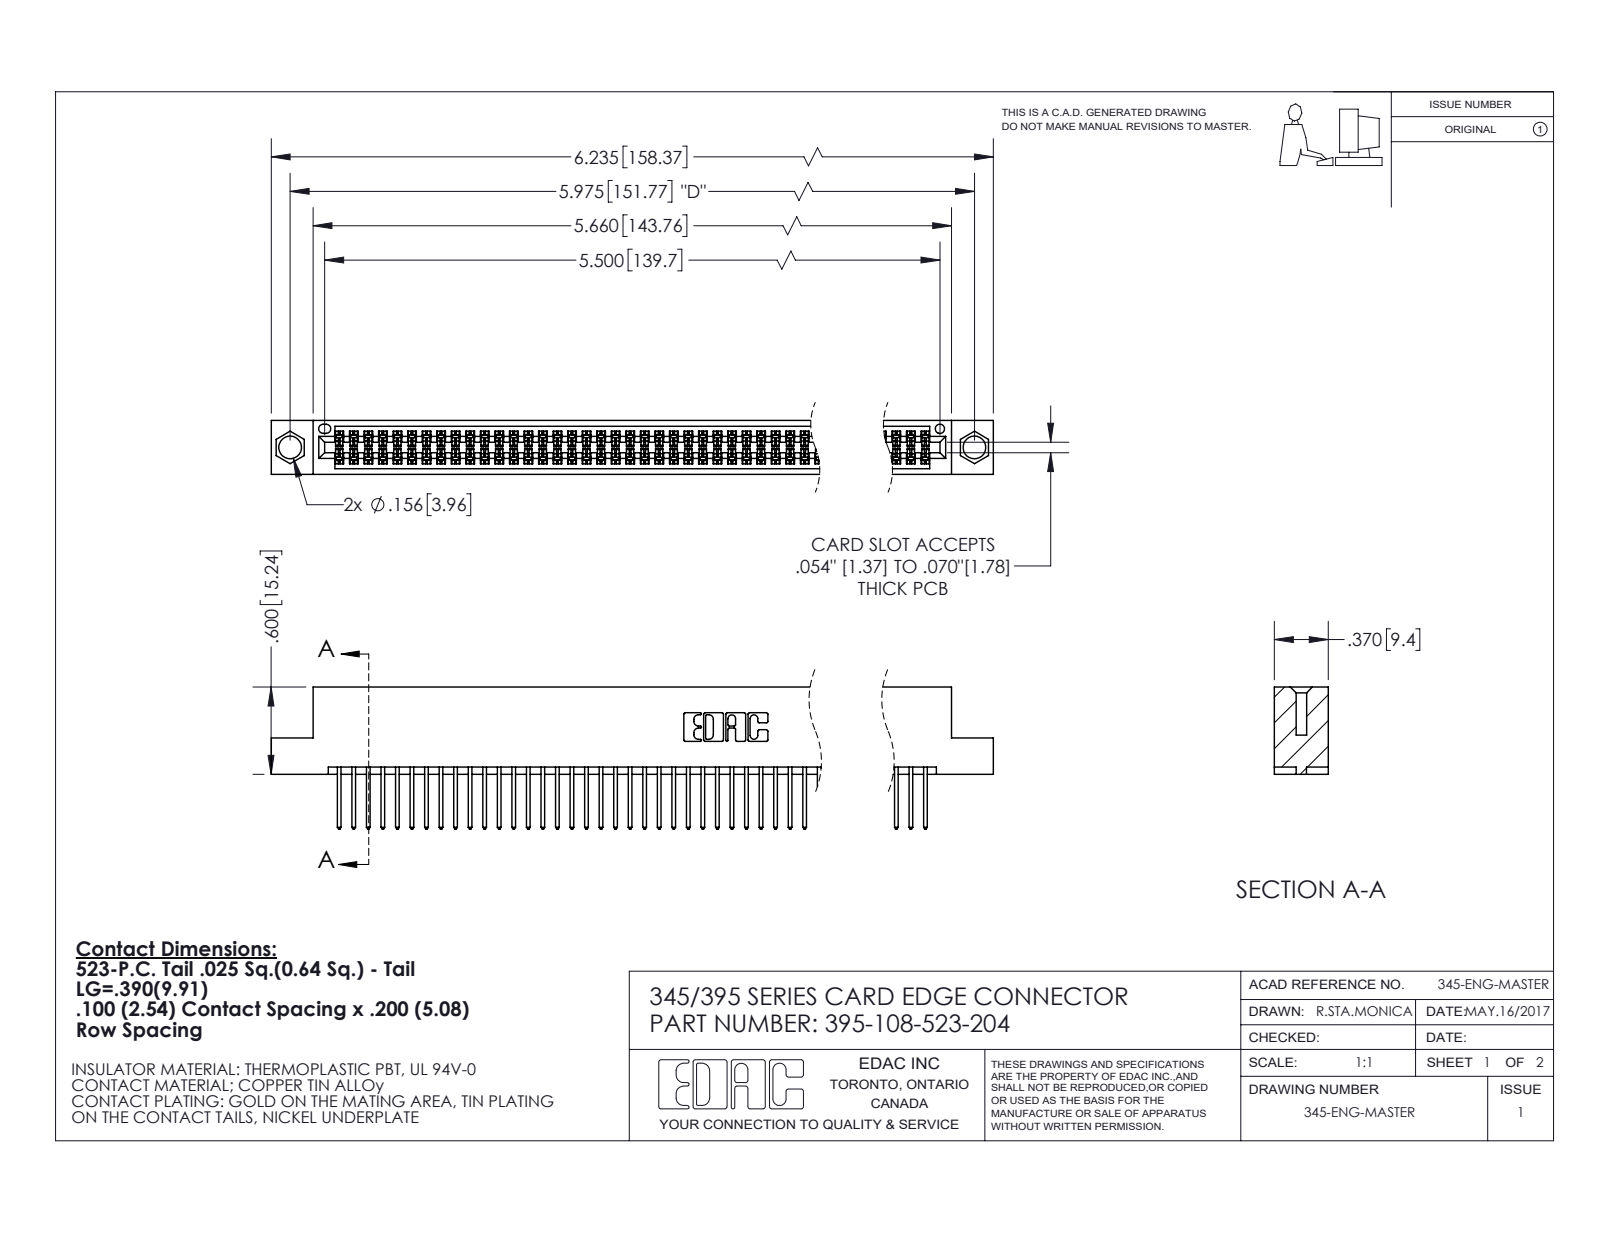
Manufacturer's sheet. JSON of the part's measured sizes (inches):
{"part_name": "395-108-523-204; 345-292-001_345-293-123; 345 Part_Flush Mounting Lugs - 0.156 Dia-TI", "step_written_by": "SolidWorks 2020 (CONFIG_CONTROL_DESIGN)", "units": "inches", "bodies": {"solids": 109, "faces": 5540, "planar": 3658, "cylindrical": 1882, "other": 0}, "overall_size": [6.235, 0.977, 0.37], "volume_in3": 0.953, "surface_area_in2": 37.44, "round_holes": [[0.156, 2], [0.064, 1]], "partial_cylinders_radius": [[0.006, 162], [0.01, 108], [0.01, 22], [0.007, 6], [0.031, 6], [0.026, 3], [0.014, 2], [0.019, 2]], "face_to_face_distances": [0.298, 0.072, 0.2, 0.098, 0.272, 0.025, 0.37, 0.225, 0.175, 0.149], "hole_center_spacings": [0.27, 5.739, 5.975]}
